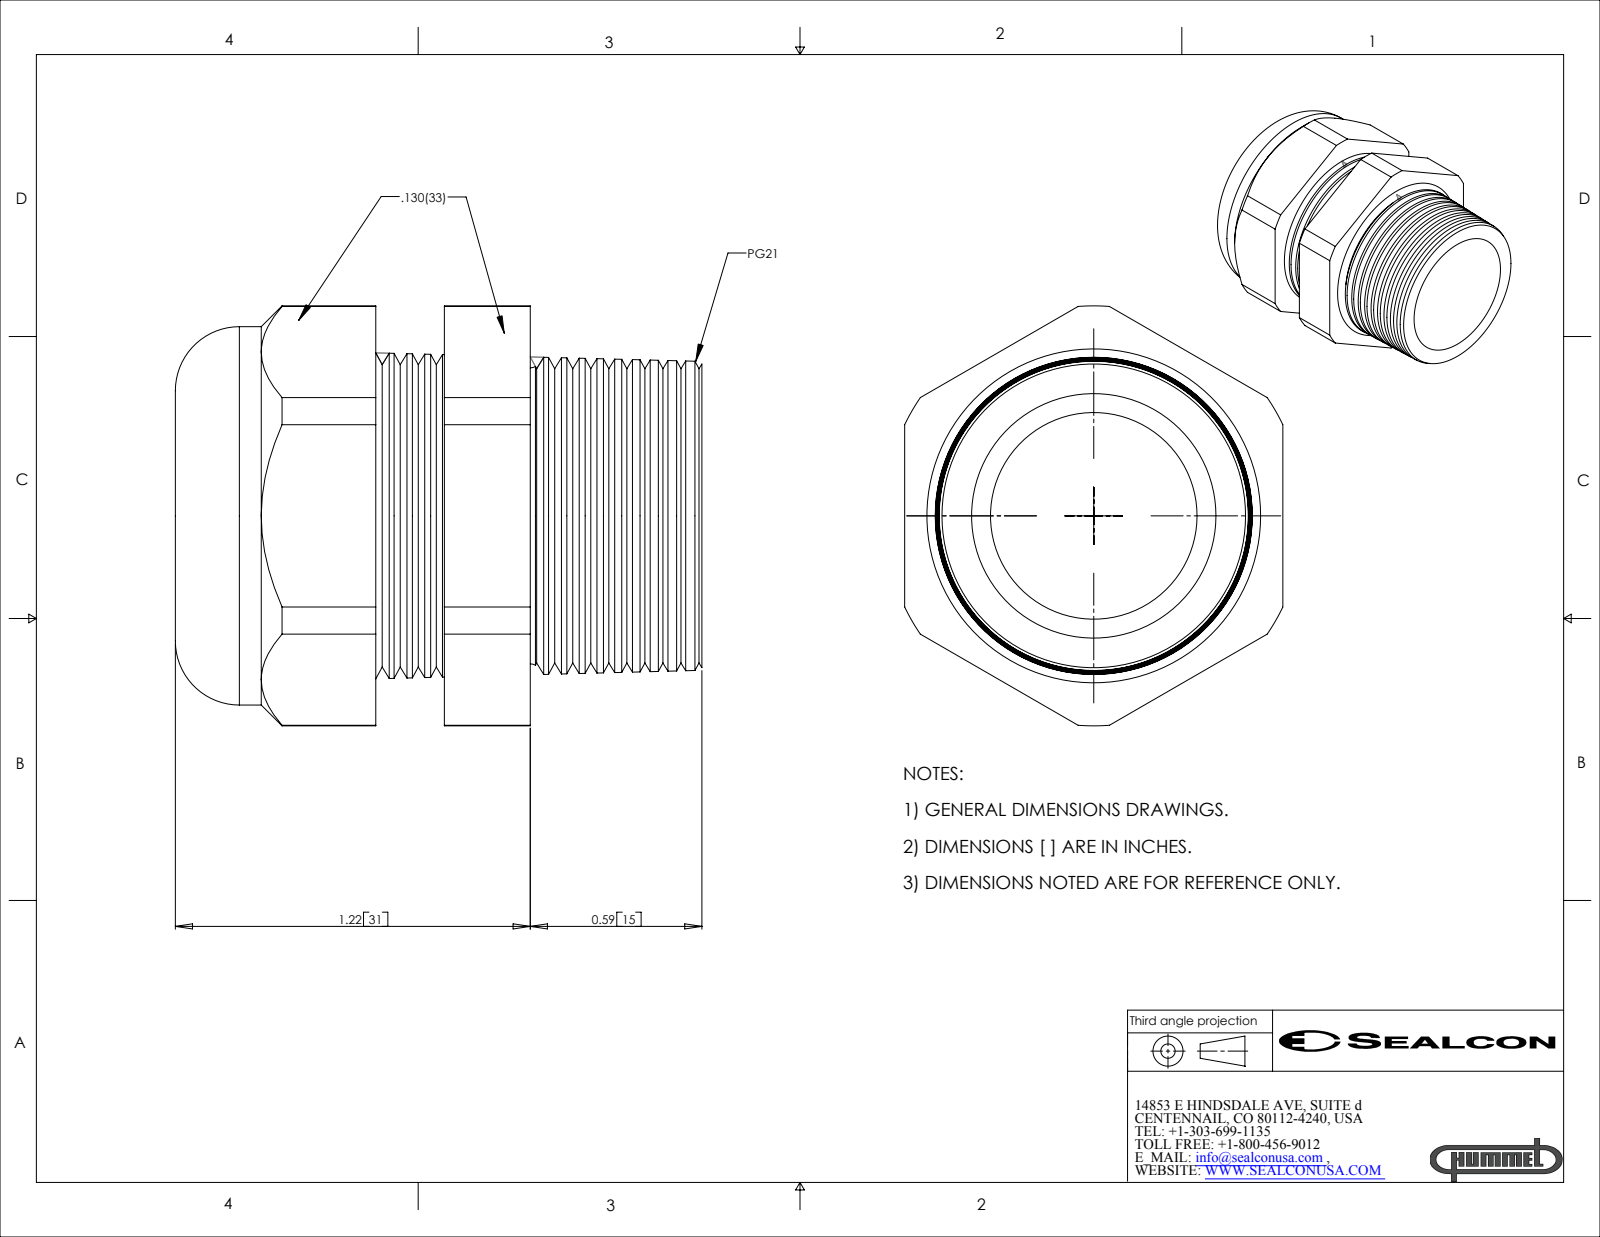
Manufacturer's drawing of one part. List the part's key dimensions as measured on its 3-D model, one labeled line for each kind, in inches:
Part name (STEP PRODUCT): CD21CA-BK
STEP written by: SolidWorks 2007 (CONFIG_CONTROL_DESIGN)
Units: inches
Bodies: 2 solids, 140 faces (20 planar, 22 cylindrical, 98 other)
Overall size (bounding box): 1.81 × 1.443 × 1.3
Volume: 1.272 in³ · Surface area: 17.32 in²
Round holes (diameter × count): ⌀0.71 ×1, ⌀0.84 ×1
Round bosses / shafts (diameter × count): ⌀1.3 ×1
Partial cylindrical surfaces — rounded edges, fillets, slot ends (radius × count): R0.721 ×1
Main face-to-face distances: 1.3, 0.236, 0.295, 0.531, 0.925, 0.394, 0.63, 1.515, 1.121, 0.885
